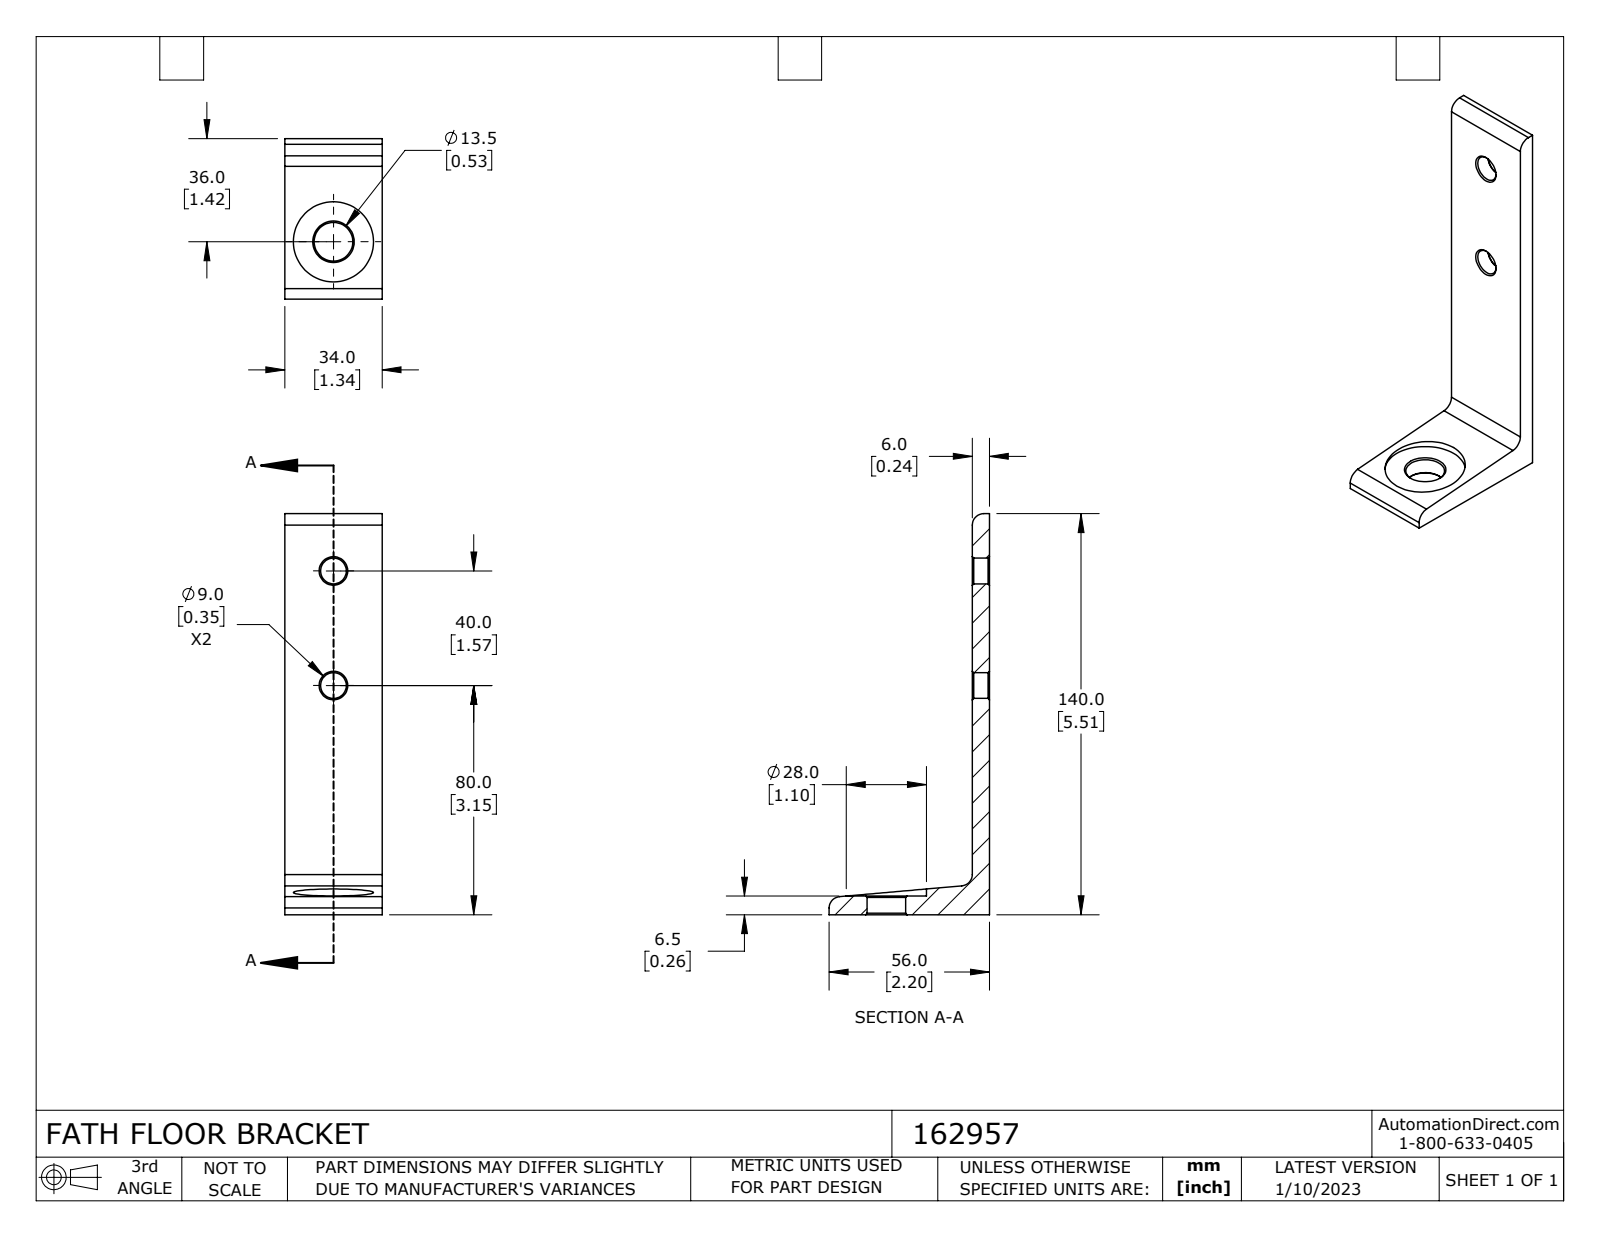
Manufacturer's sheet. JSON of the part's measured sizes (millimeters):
{"part_name": "162957", "step_written_by": "SolidWorks 2021 (CONFIG_CONTROL_DESIGN)", "units": "millimeters", "bodies": {"solids": 1, "faces": 32, "planar": 9, "cylindrical": 11, "other": 12}, "overall_size": [140, 56, 34], "volume_mm3": 39870, "surface_area_mm2": 15650, "round_holes": [[9, 2], [13.5, 1], [28, 1]], "partial_cylinders_radius": [[4, 3]], "face_to_face_distances": [6, 34, 6.5, 56, 50, 140, 133.5], "hole_center_spacings": [40]}
